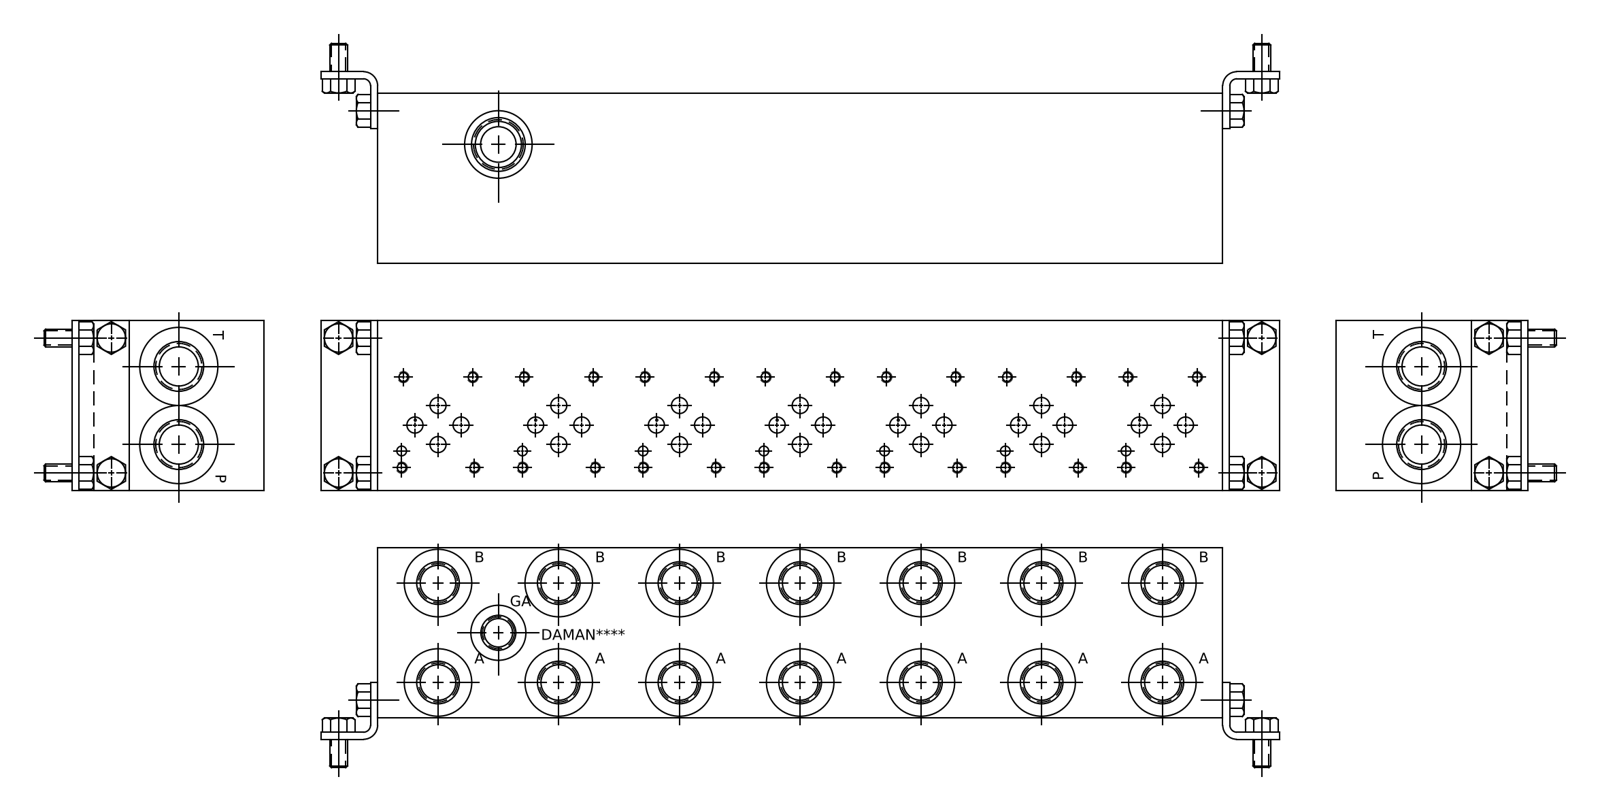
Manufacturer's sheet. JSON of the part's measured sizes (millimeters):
{"part_name": "Part_AD03P072S_C_3D", "step_written_by": "Autodesk Inventor 2020 (AUTOMOTIVE_DESIGN)", "units": "millimeters", "bodies": {"solids": 1, "faces": 1120, "planar": 534, "cylindrical": 200, "other": 386}, "overall_size": [377.82, 76.2, 76.2], "volume_mm3": 2025000, "surface_area_mm2": 167818, "round_holes": [[3.78, 28], [4.83, 28], [7.14, 21], [15.88, 14], [17.5, 14], [19.05, 14], [19.25, 14], [30.63, 14], [3.96, 7], [6.35, 7], [22.23, 3], [6.53, 2]], "face_to_face_distances": [76.2, 0.79, 75.41, 377.82, 377.04, 0.78, 376.25, 377.03, 15.06, 14.27], "hole_center_spacings": [107.95, 53.98, 215.9, 53.97, 161.93, 118.61, 116.74, 161.92]}
